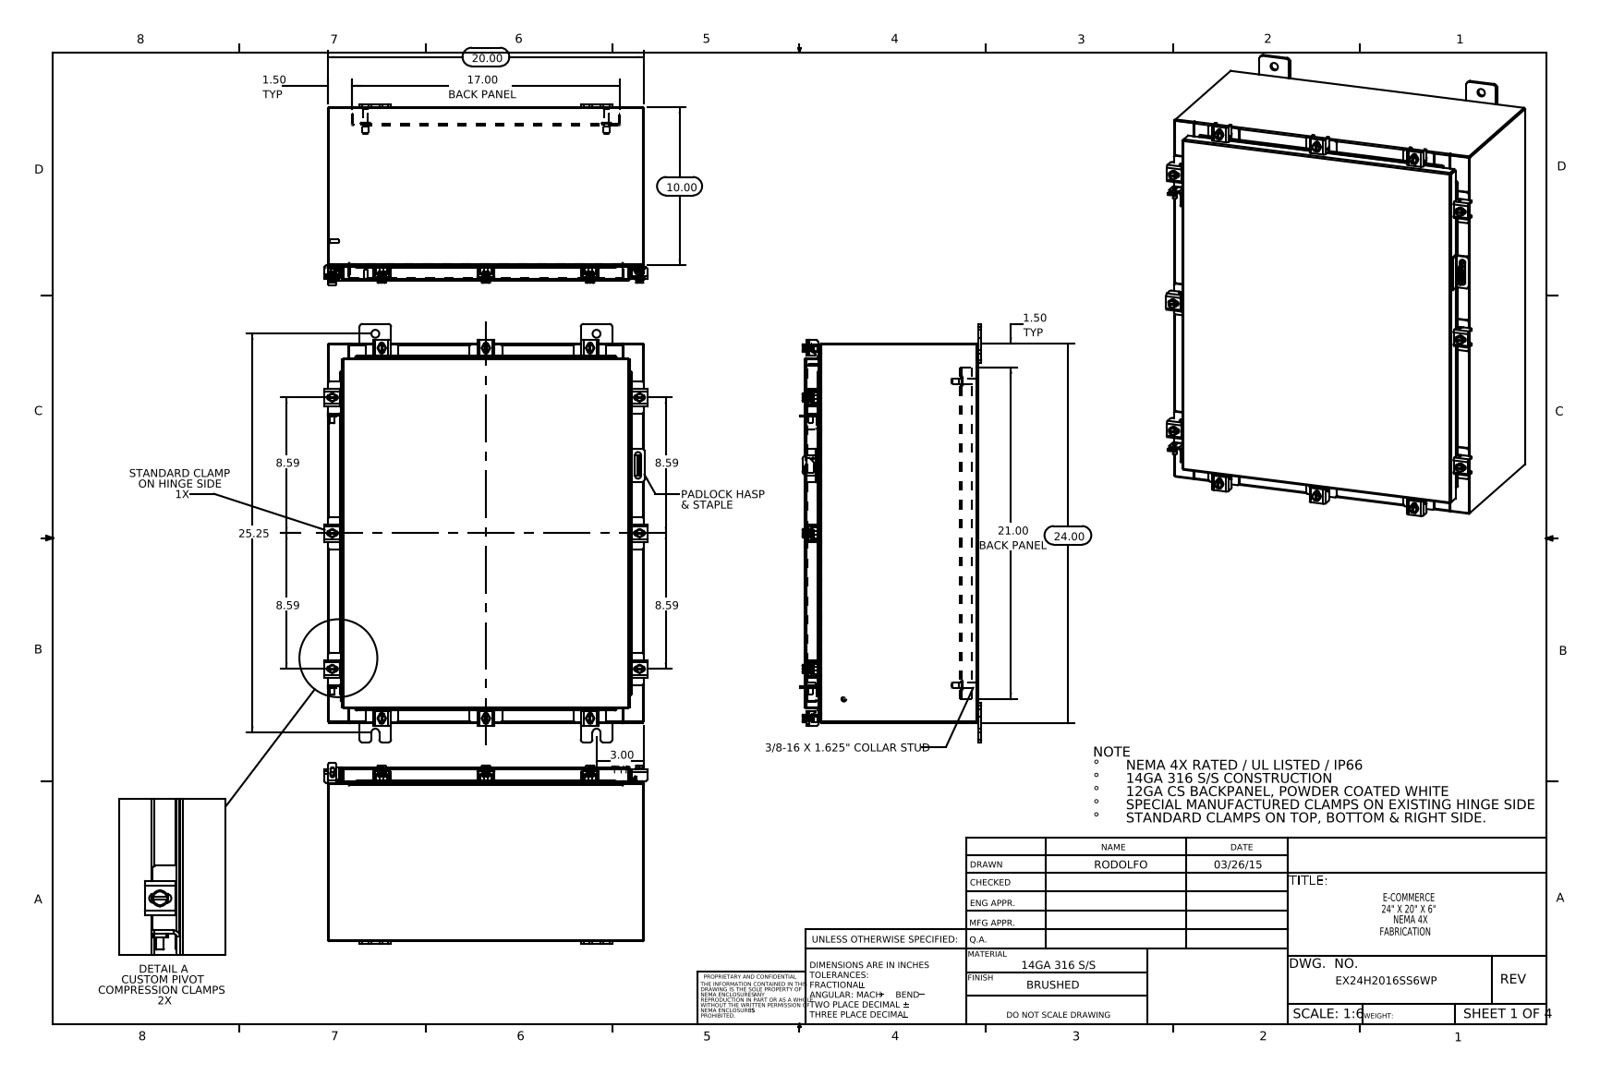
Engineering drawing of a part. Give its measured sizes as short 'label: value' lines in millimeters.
name: ATEX CLAMP HINGE BRAKET; HW-CLN-NH-20330; EX24H2016SSWP Backpanel; EX24H2016SSWP Special Clamp (+8 more)
written by: SolidWorks 2014 (CONFIG_CONTROL_DESIGN)
unit: mm
bodies: 81 solids, 2018 faces (1075 planar, 783 cylindrical, 160 other)
size: 673.1 × 518.7 × 290.9
volume: 3 282 000 mm³; area: 3 250 000 mm²
holes: 12× ⌀5.4, 12× ⌀6.6, 8× ⌀12.7, 1× ⌀3.2, 1× ⌀6.4
bosses: 12× ⌀12.7, 12× ⌀6.4, 10× ⌀10.1, 4× ⌀15.9, 4× ⌀9.5, 4× ⌀8.4, 2× ⌀8, 2× ⌀6
rounds: 54× R1.5, 24× R0.3, 24× R3.6, 24× R4.8, 22× R2.2, 22× R3, 18× R2.3, 17× R1.3
face distances: 1.9, 276.9, 506.1, 278.8, 275, 607.7, 2.6, 25.4, 27.3, 249.6
hole spacings: 59.4, 112.5, 167.5, 218.3, 259.5, 308.3, 386.9, 422.1
